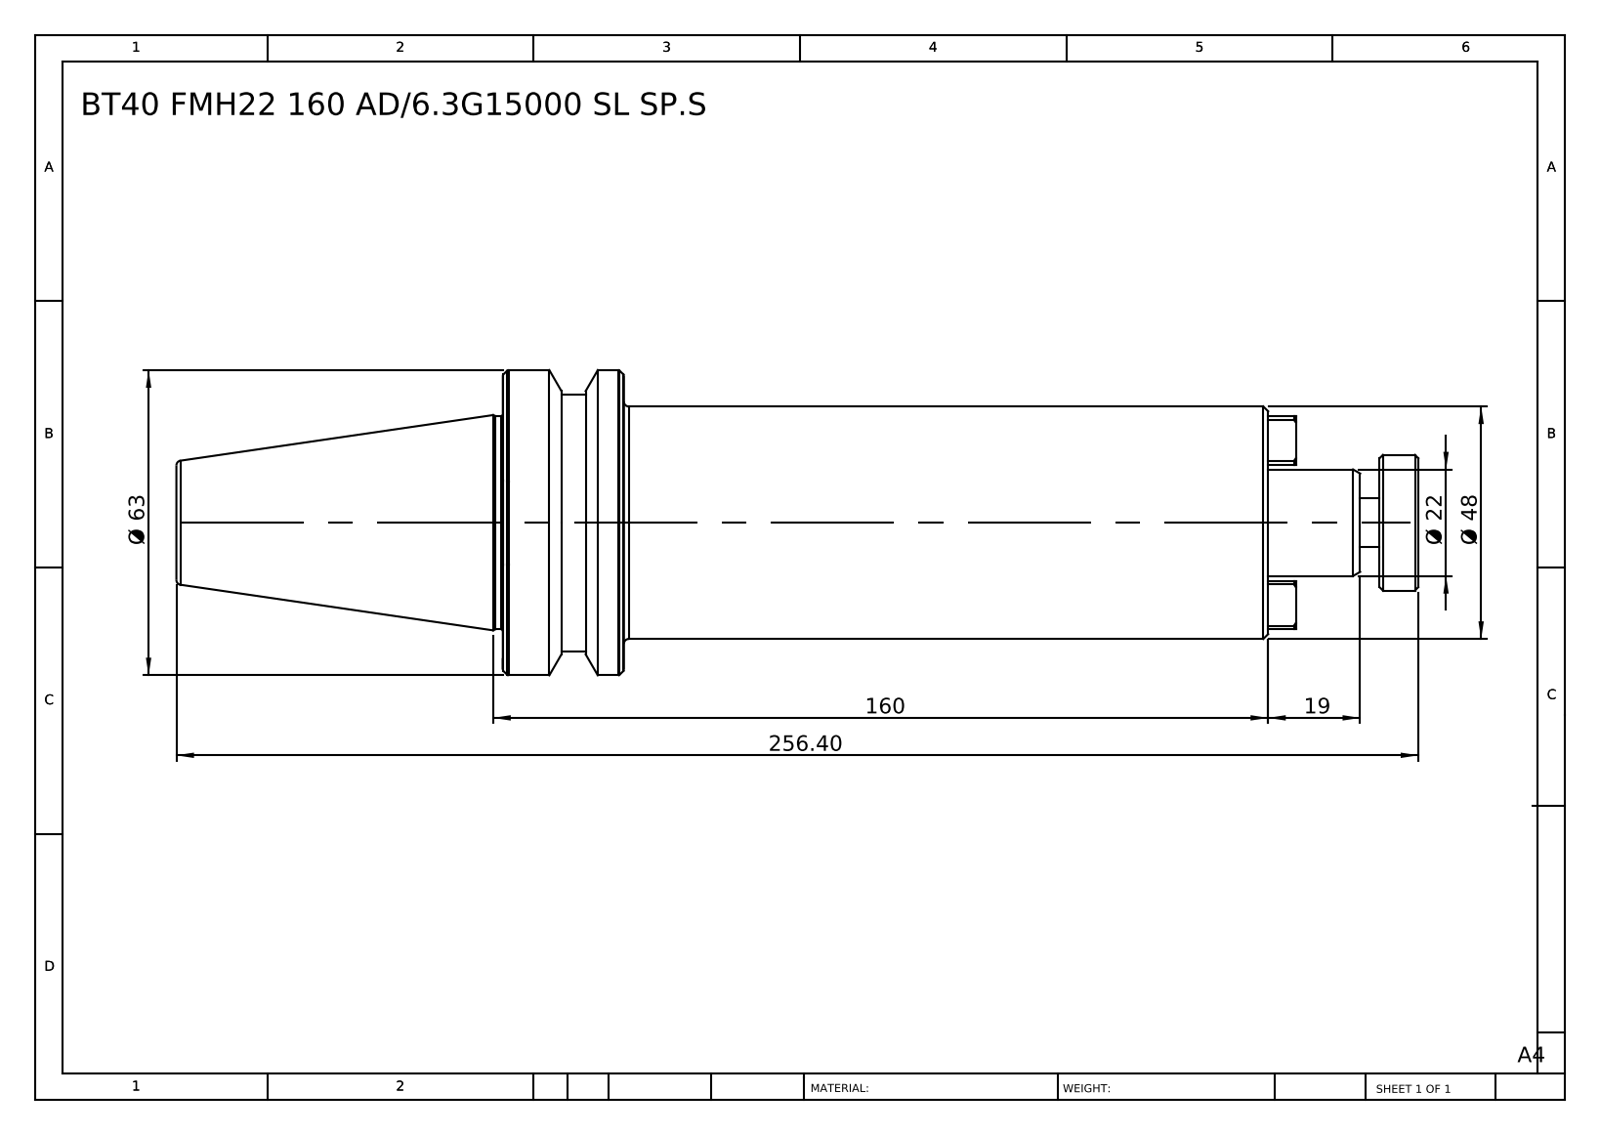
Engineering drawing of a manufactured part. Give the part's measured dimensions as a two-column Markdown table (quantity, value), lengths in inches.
| quantity | value |
| --- | --- |
| part name | BT40 FMH22 160 AD-6.3G15000 SL SP.S |
| STEP written by | SolidWorks 2014 (CONFIG_CONTROL_DESIGN) |
| units | inches |
| bodies | 1 solid, 91 faces (35 planar, 16 cylindrical, 40 other) |
| overall size | 10.094 × 2.48 × 2.48 |
| volume | 23.95 in³ |
| surface area | 64.73 in² |
| round bosses / shafts (diameter × count) | 2.48 × 1, 2.087 × 1, 1.89 × 1, 1.732 × 1, 1.102 × 1, 0.866 × 1, 0.394 × 1 |
| main face-to-face distances | 6.22, 5.236, 0.984, 1.22, 6.457, 7.441, 0.315, 0.906, 6.142, 7.126 |
